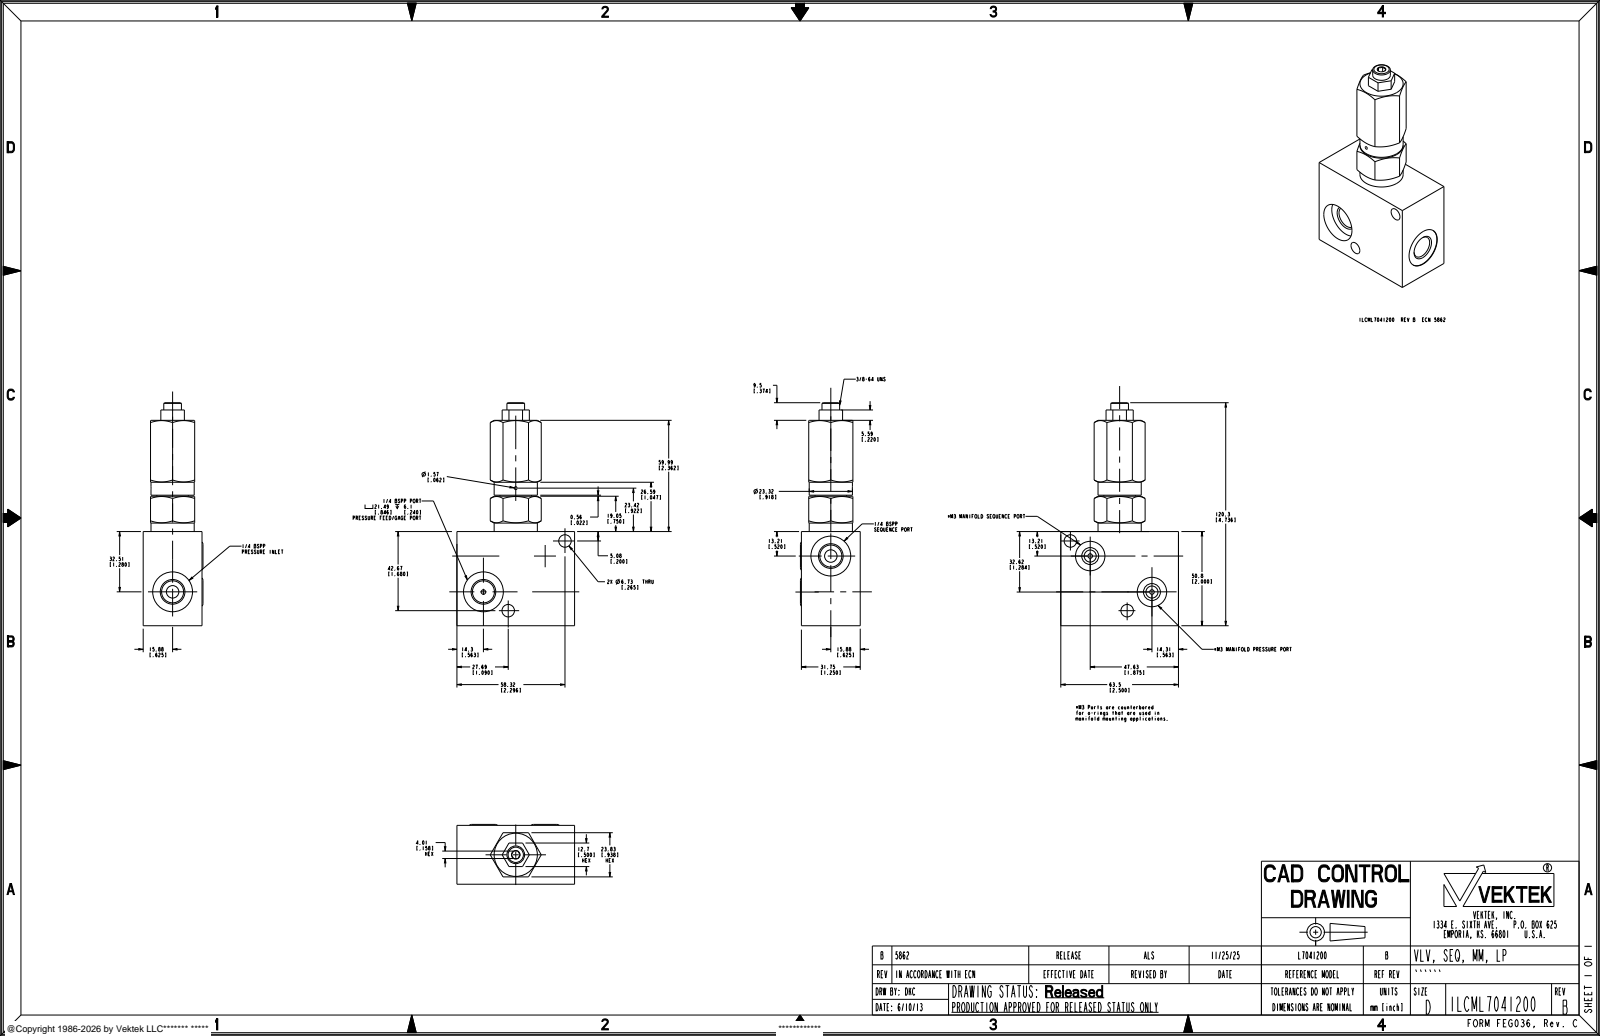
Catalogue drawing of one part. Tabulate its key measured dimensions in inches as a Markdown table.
| quantity | value |
| --- | --- |
| part name | ILCML7041200 |
| STEP written by | CREO PARAMETRIC BY PTC INC, 2021164 (AUTOMOTIVE_DESIGN) |
| units | inches |
| bodies | 1 solid, 138 faces (50 planar, 52 cylindrical, 36 other) |
| overall size | 4.736 × 2.5 × 1.27 |
| volume | 7.258 in³ |
| surface area | 40.6 in² |
| round holes (diameter × count) | 0.265 × 4, 0.468 × 3, 0.098 × 2, 0.256 × 2, 0.625 × 2, 0.846 × 2, 0.062 × 1, 0.846 × 1 |
| round bosses / shafts (diameter × count) | 0.518 × 3, 0.918 × 1, 0.67 × 1, 0.375 × 1 |
| main face-to-face distances | 1.25, 0.938, 2, 0.156, 1.094, 2.5, 2.49, 4.362, 2.362, 0.219 |
| hole center spacings | 0.529, 0.659, 0.661, 0.76, 1.4, 1.517, 1.518, 1.534 |
